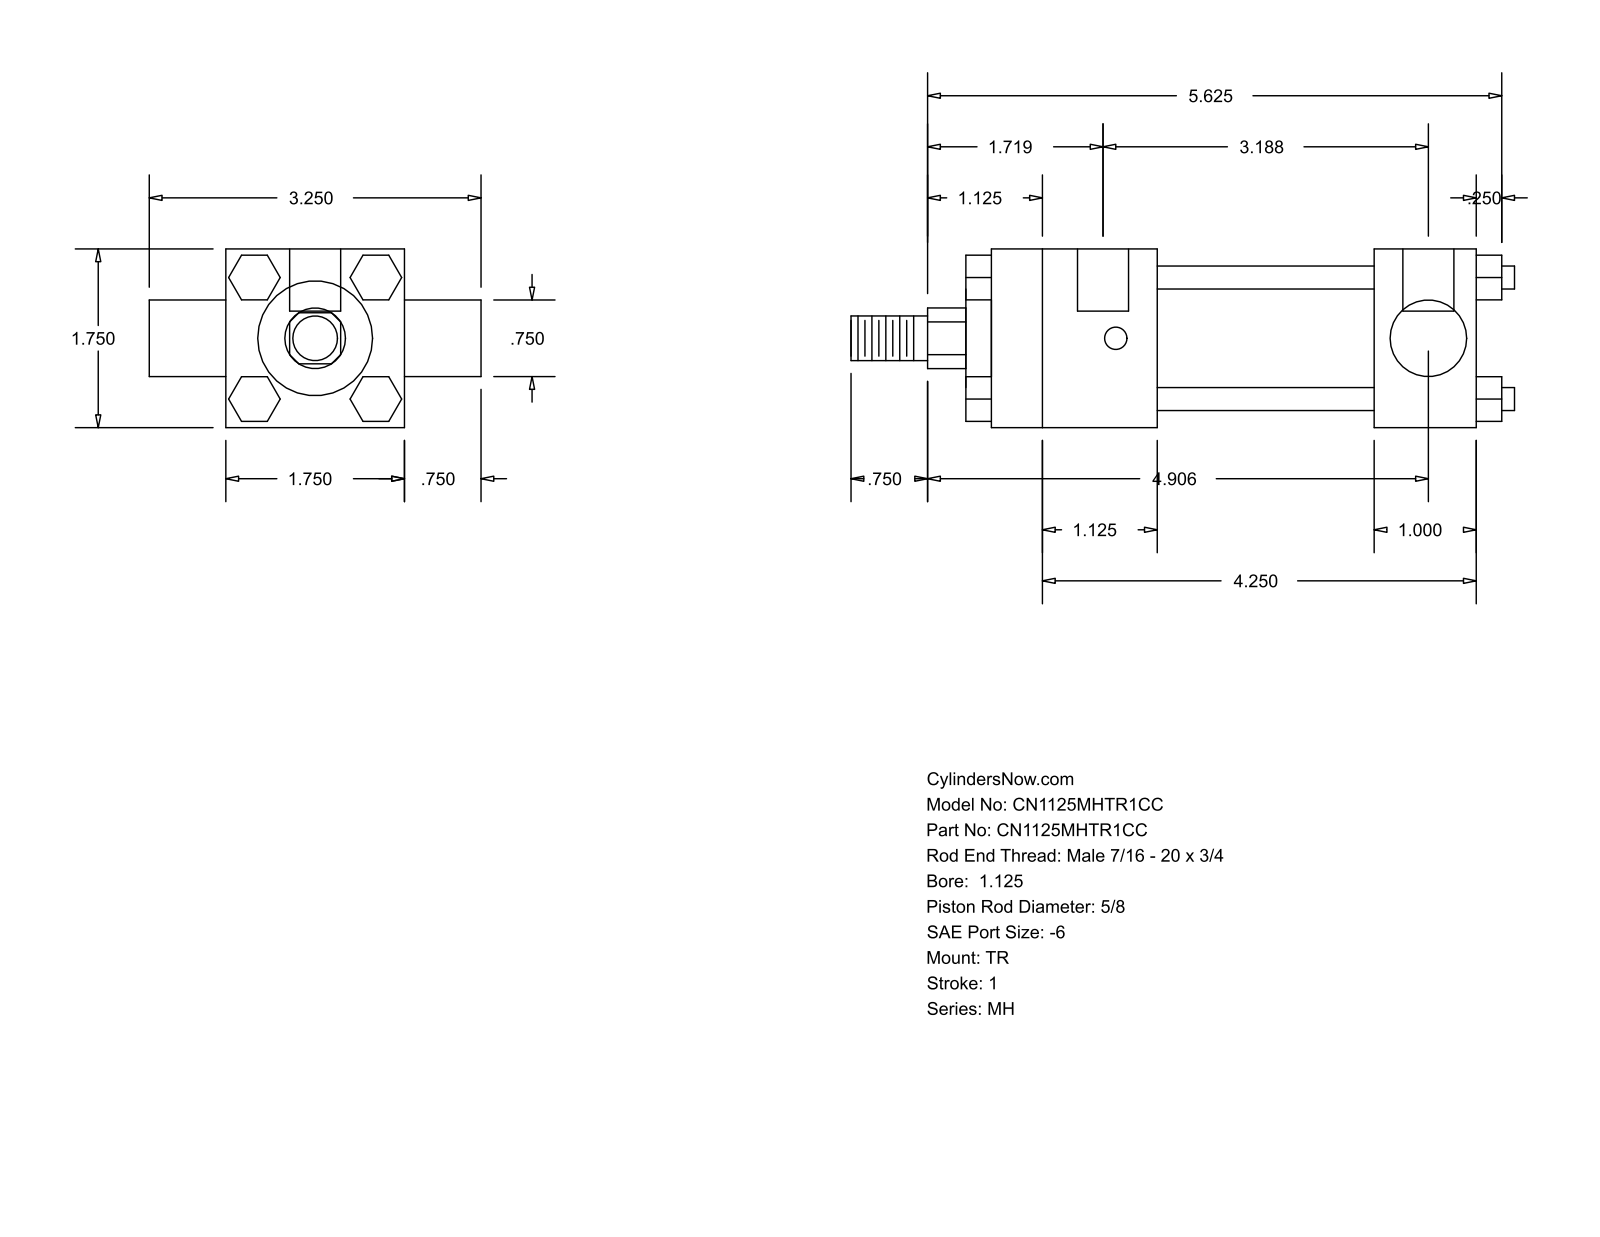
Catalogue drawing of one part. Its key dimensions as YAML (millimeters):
part_name: "MH_TR__0112_0.625"
step_written_by: "GSSL Pune (CONFIG_CONTROL_DESIGN)"
units: millimeters
bodies: {solids: 0, faces: 120, planar: 92, cylindrical: 28, other: 0}
overall_size: [165.1, 82.55, 44.45]
round_holes:
  - {diameter: 5.56, count: 3}
  - {diameter: 12.7, count: 2}
round_bosses_or_shafts:
  - {diameter: 5.71, count: 4}
  - {diameter: 34.92, count: 1}
  - {diameter: 28.57, count: 1}
  - {diameter: 19.05, count: 1}
  - {diameter: 15.88, count: 1}
  - {diameter: 11.11, count: 1}
partial_cylinders:
  - {radius: 7.54, count: 1}
face_to_face_distances: [44.46, 6.35, 127, 11.11, 53.97, 79.38, 25.41, 41.27, 95.24, 120.65]
hole_center_spacings: [3.17, 77.79, 80.96]
